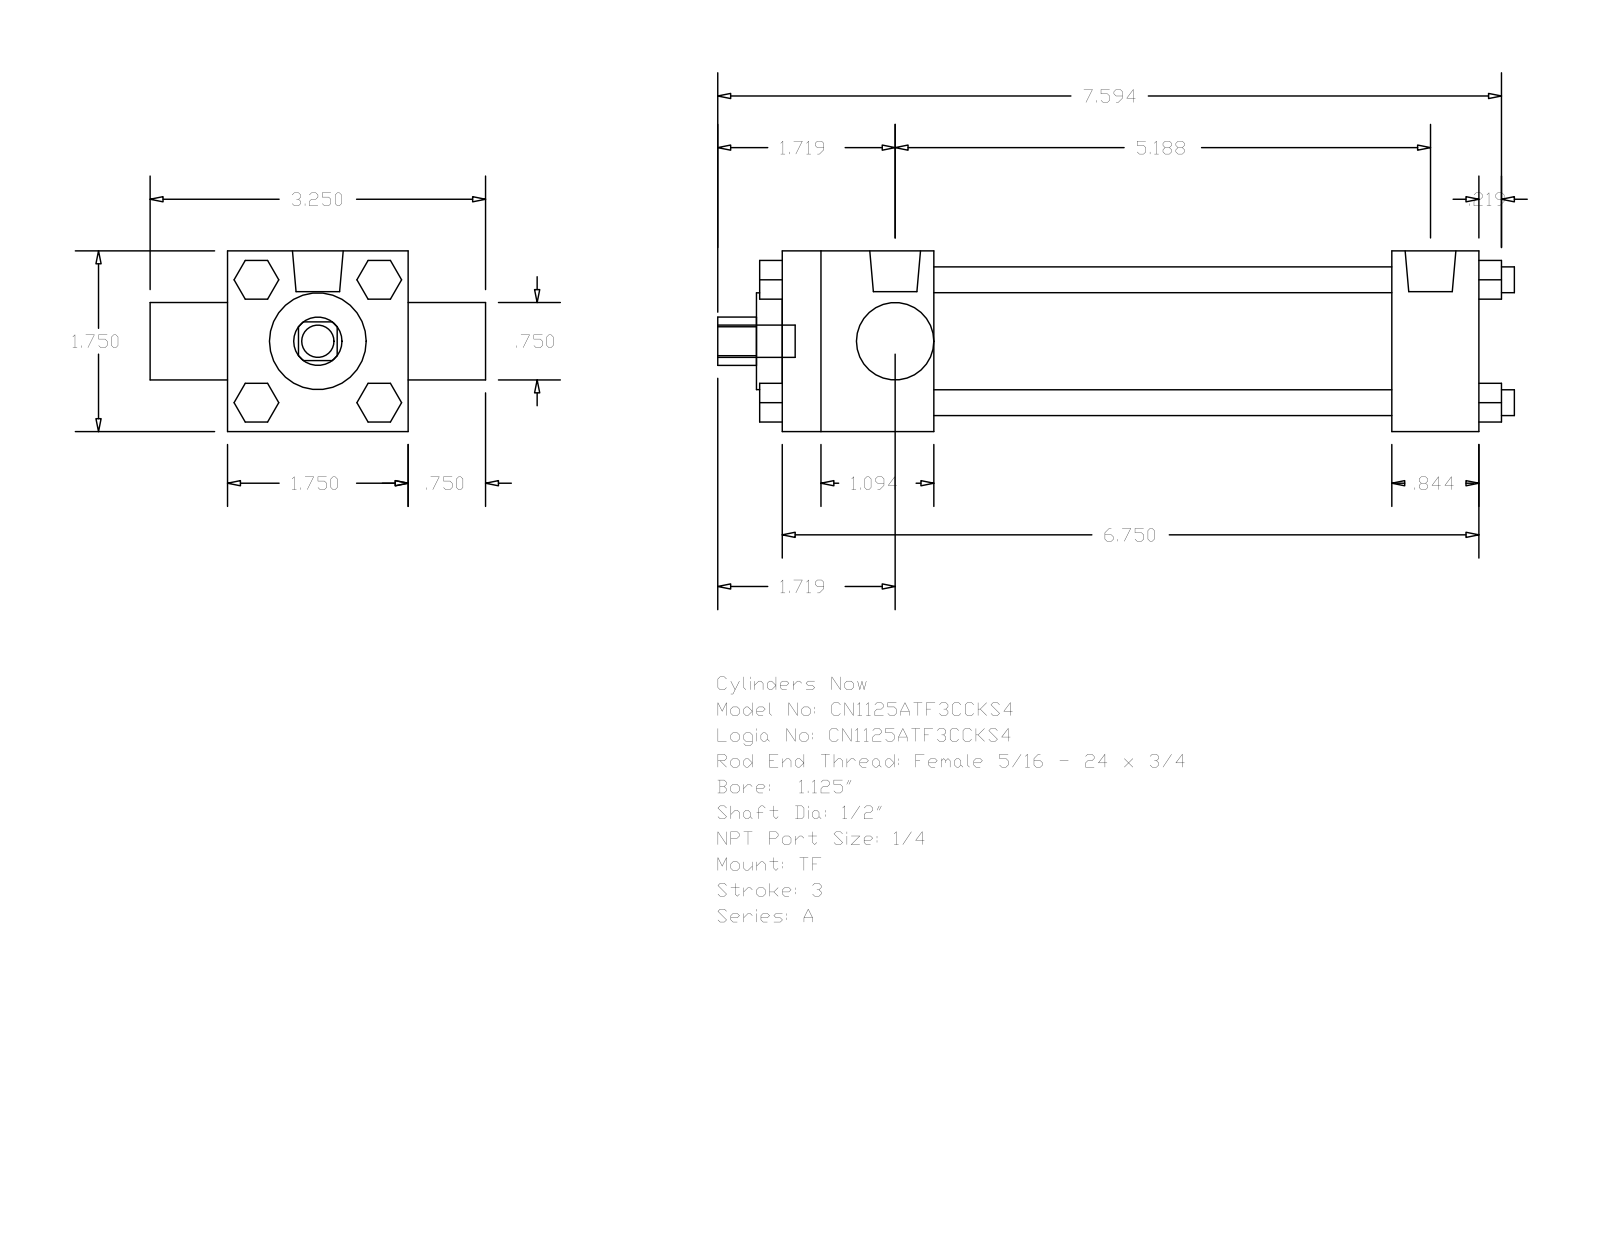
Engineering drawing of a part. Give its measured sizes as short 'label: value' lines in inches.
name: A_TF__0112_0.5
written by: GSSL Pune (CONFIG_CONTROL_DESIGN)
unit: in
bodies: 0 solids, 120 faces (92 planar, 28 cylindrical, 0 other)
size: 7.719 × 3.25 × 1.75
holes: 1× ⌀0.5, 1× ⌀0.75, 1× ⌀0.937, 1× ⌀1.255
bosses: 4× ⌀0.25, 3× ⌀0.219, 2× ⌀0.492, 1× ⌀0.313
rounds: 1× R0.234
face distances: 1.75, 6.75, 5.906, 0.844, 1.469, 4.437, 5.281, 0.75, 2.5, 0.375
